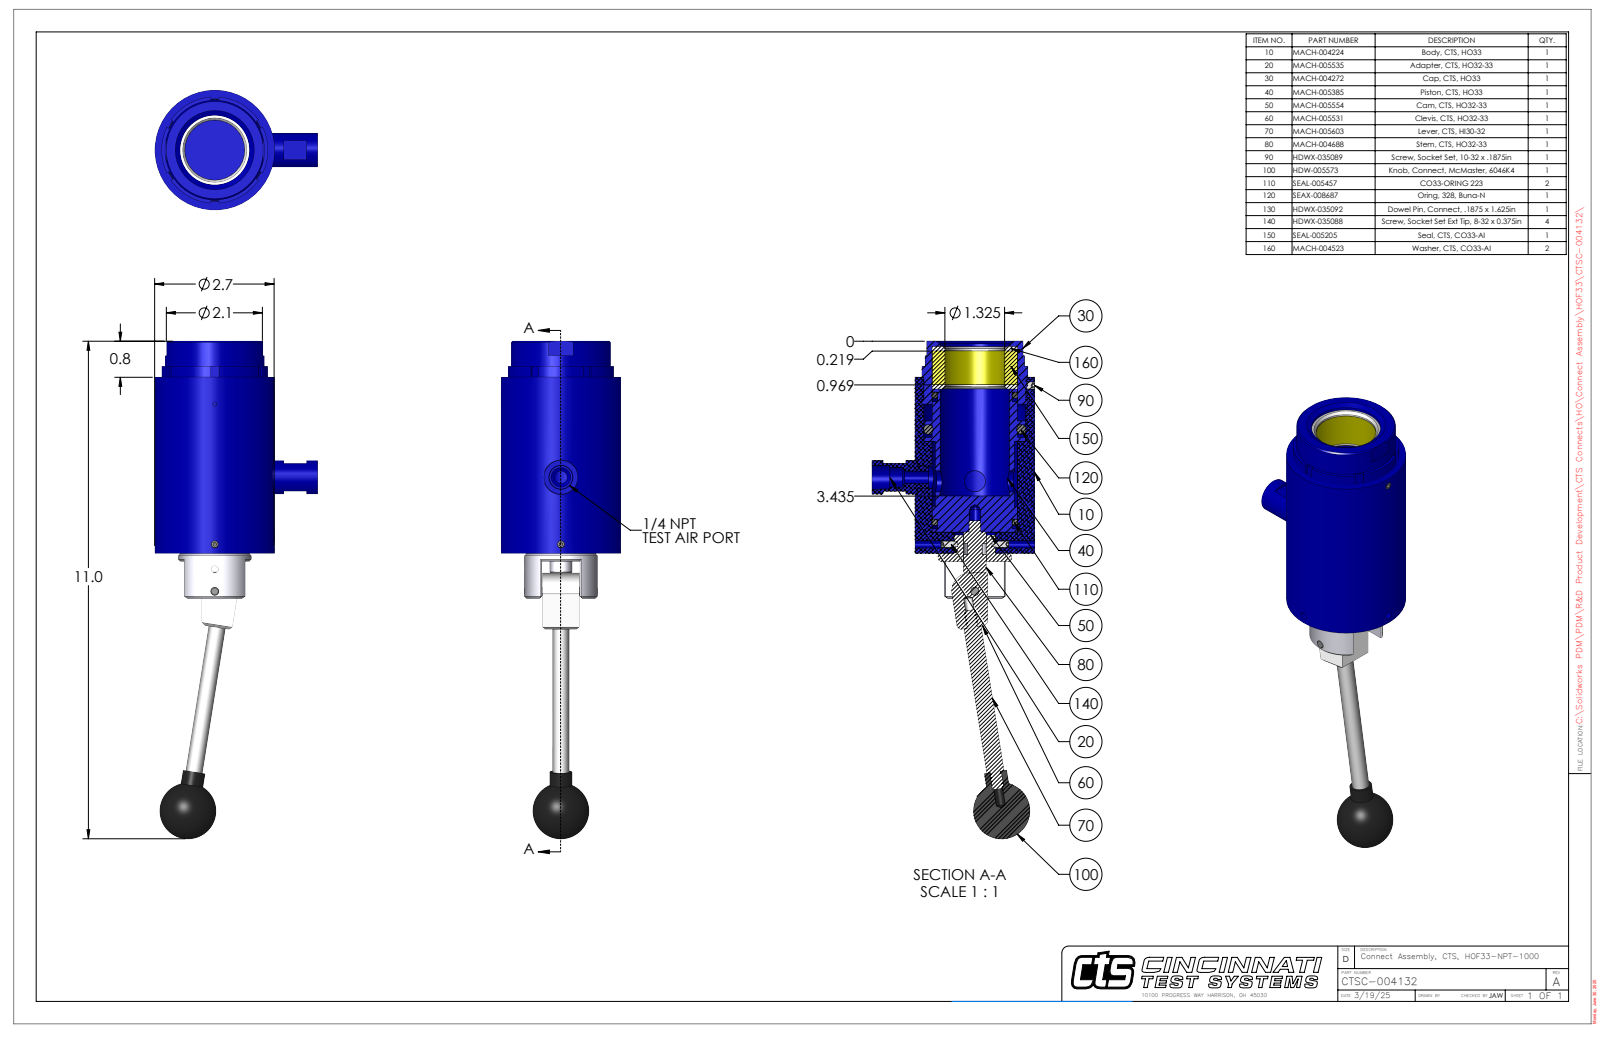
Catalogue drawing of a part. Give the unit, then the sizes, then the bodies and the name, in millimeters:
Units: millimetres
Overall size (bounding box): 280.3 × 91.4 × 67.3
Round holes (diameter × count): ⌀5.1 ×3, ⌀4 ×2, ⌀11.9 ×2, ⌀2.4 ×1, ⌀4.8 ×1, ⌀4.8 ×1, ⌀6.4 ×1, ⌀7.1 ×1, ⌀11.1 ×1, ⌀12.7 ×1, ⌀13.1 ×1, ⌀13.5 ×1
Round bosses / shafts (diameter × count): ⌀19.1 ×2, ⌀12.7 ×2, ⌀4.2 ×2, ⌀2.8 ×2, ⌀67.3 ×1, ⌀59.5 ×1, ⌀55.9 ×1, ⌀47.9 ×1
Partial cylindrical surfaces — rounded edges, fillets, slot ends (radius × count): R9.8 ×1, R10.2 ×1, R28.7 ×1, R31 ×1
Main face-to-face distances: 21.4, 2.4, 19.1, 95, 114, 116.4, 92.6, 23.8, 32.3, 60.2
Hole centre spacings: 2.3, 12.4, 43.4, 49.5, 51.6, 53.9, 61.9, 92.9
Volume: 356 400 mm³ · Surface area: 86 000 mm²
Bodies: 14 solids, 542 faces (178 planar, 223 cylindrical, 141 other)
Part name (STEP PRODUCT): CTSC-004132
STEP written by: SolidWorks 2023 (AUTOMOTIVE_DESIGN)
